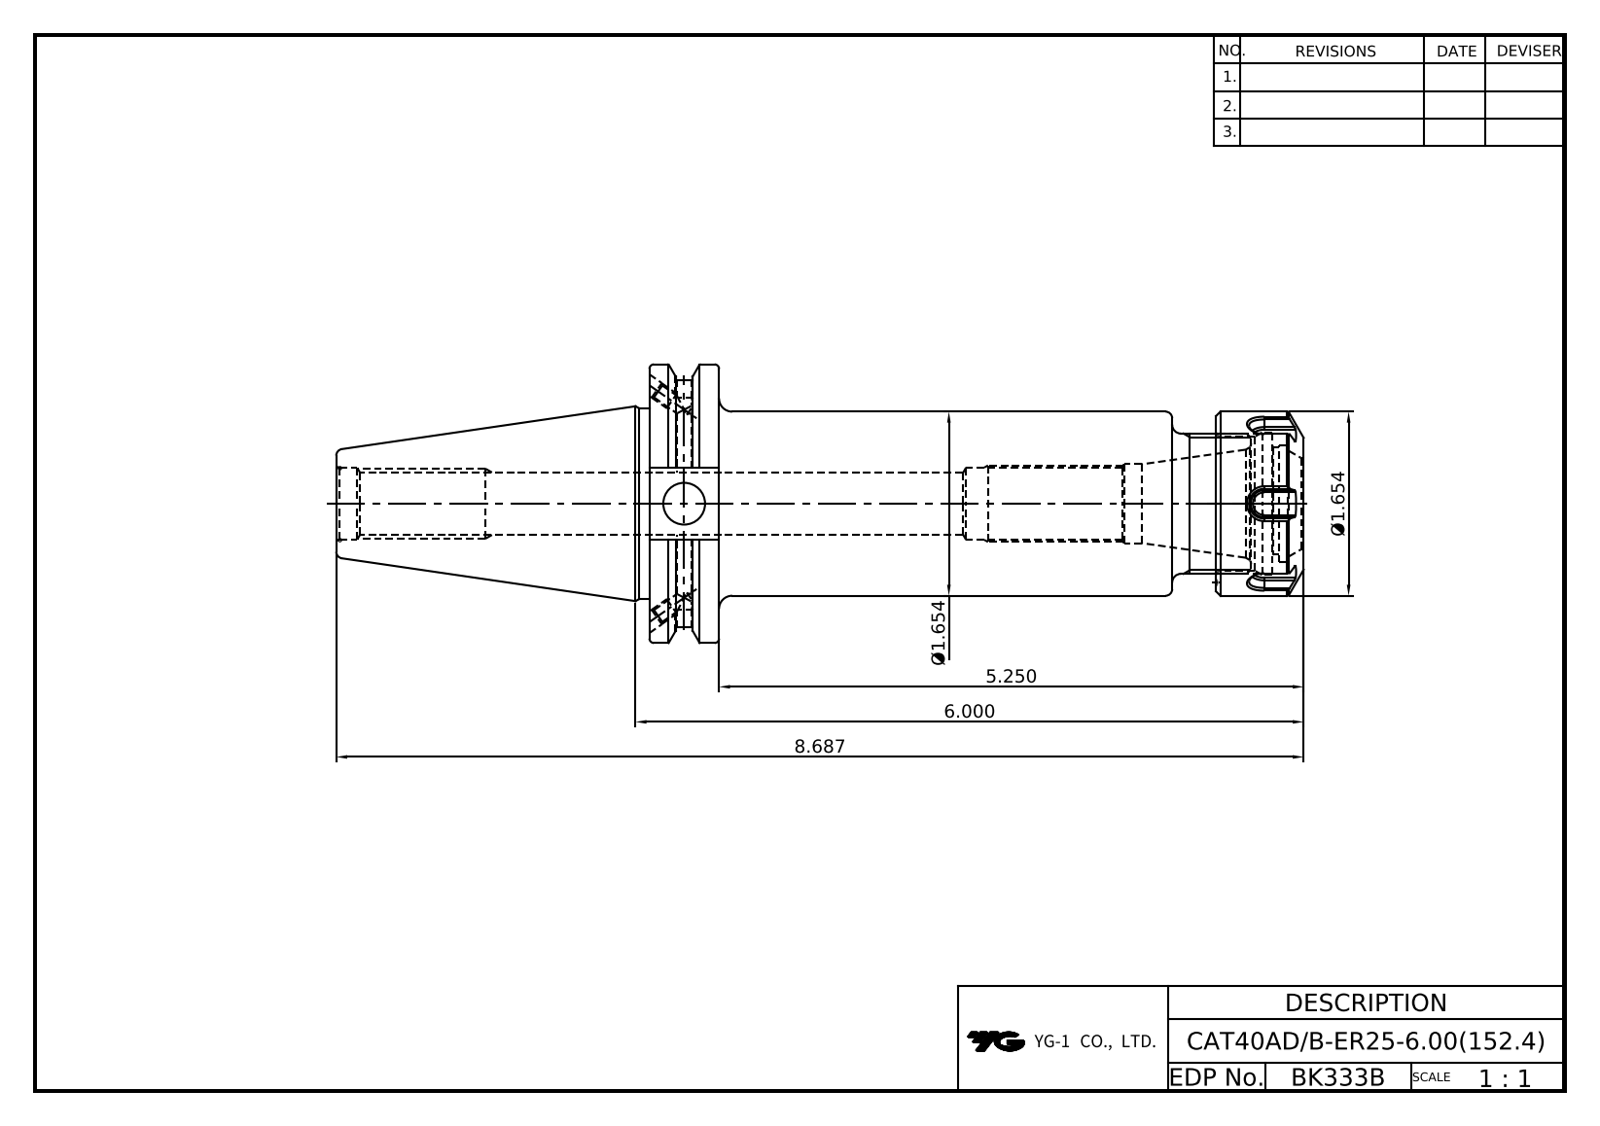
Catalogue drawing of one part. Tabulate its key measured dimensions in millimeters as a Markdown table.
| quantity | value |
| --- | --- |
| part name | LO-CAT40ADB-ER25-6.00; ER25NUT |
| STEP written by | Autodesk Inventor 2025 (AUTOMOTIVE_DESIGN) |
| units | millimeters |
| bodies | 2 solids, 170 faces (73 planar, 46 cylindrical, 51 other) |
| overall size | 220.65 × 63.5 × 61.09 |
| volume | 245 616 mm³ |
| surface area | 48 233 mm² |
| round holes (diameter × count) | 3.24 × 4, 4 × 2, 4.2 × 2, 9.53 × 1, 13.39 × 1, 15.75 × 1, 16.3 × 1, 18 × 1, 20.9 × 1, 23 × 1, 26.8 × 1, 30.5 × 1 |
| round bosses / shafts (diameter × count) | 63.5 × 1, 43.6 × 1, 42 × 1, 32 × 1 |
| partial cylindrical surfaces (radius × count) | 0.5 × 12, 28.15 × 1 |
| main face-to-face distances | 15.88, 129.23, 113.35, 142.13, 126.25, 12.9, 149.23, 133.35, 20, 7.1 |
